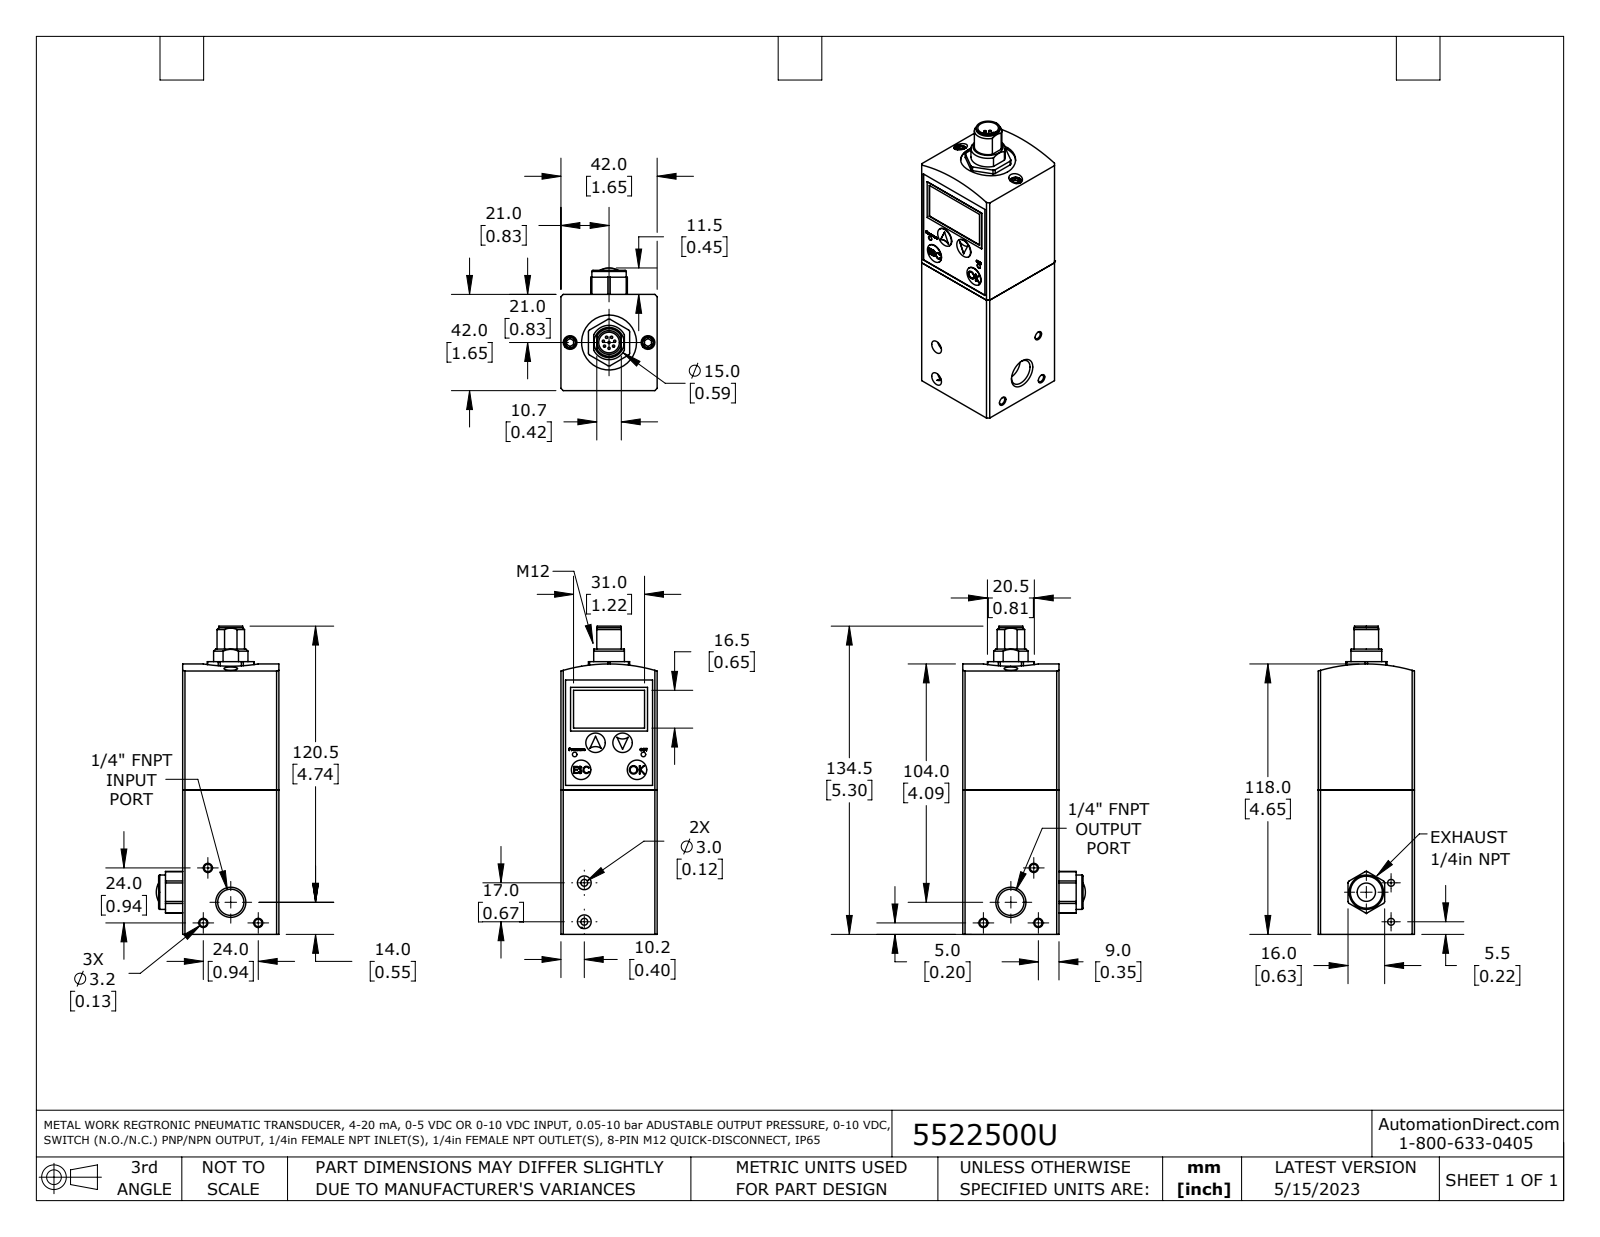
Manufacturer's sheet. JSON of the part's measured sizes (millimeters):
{"part_name": "5522500U", "step_written_by": "SolidWorks 2021 (AUTOMOTIVE_DESIGN)", "units": "millimeters", "bodies": {"solids": 1, "faces": 538, "planar": 243, "cylindrical": 248, "other": 47}, "overall_size": [134.5, 53.5, 42], "volume_mm3": 206800, "surface_area_mm2": 27250, "round_holes": [[6, 8], [3.3, 3], [0.8, 2], [2, 2], [3, 2], [1, 1], [3.7, 1], [9, 1], [11.5, 1], [24, 1]], "round_bosses_or_shafts": [[1, 8], [5, 6], [8.5, 4], [0.6, 2], [15, 1], [10.4, 1], [3, 1], [0.8, 1]], "partial_cylinders_radius": [[1, 12], [0.2, 4], [0.2, 3], [0.1, 2], [0.1, 2], [0.1, 2], [0.1, 2], [0.2, 2]], "face_to_face_distances": [42, 41.8, 0.4, 41.6, 58, 7, 63, 35, 42, 0.4], "hole_center_spacings": [17.2, 22.4, 35.9, 17, 34, 15, 29.2, 44.8]}
